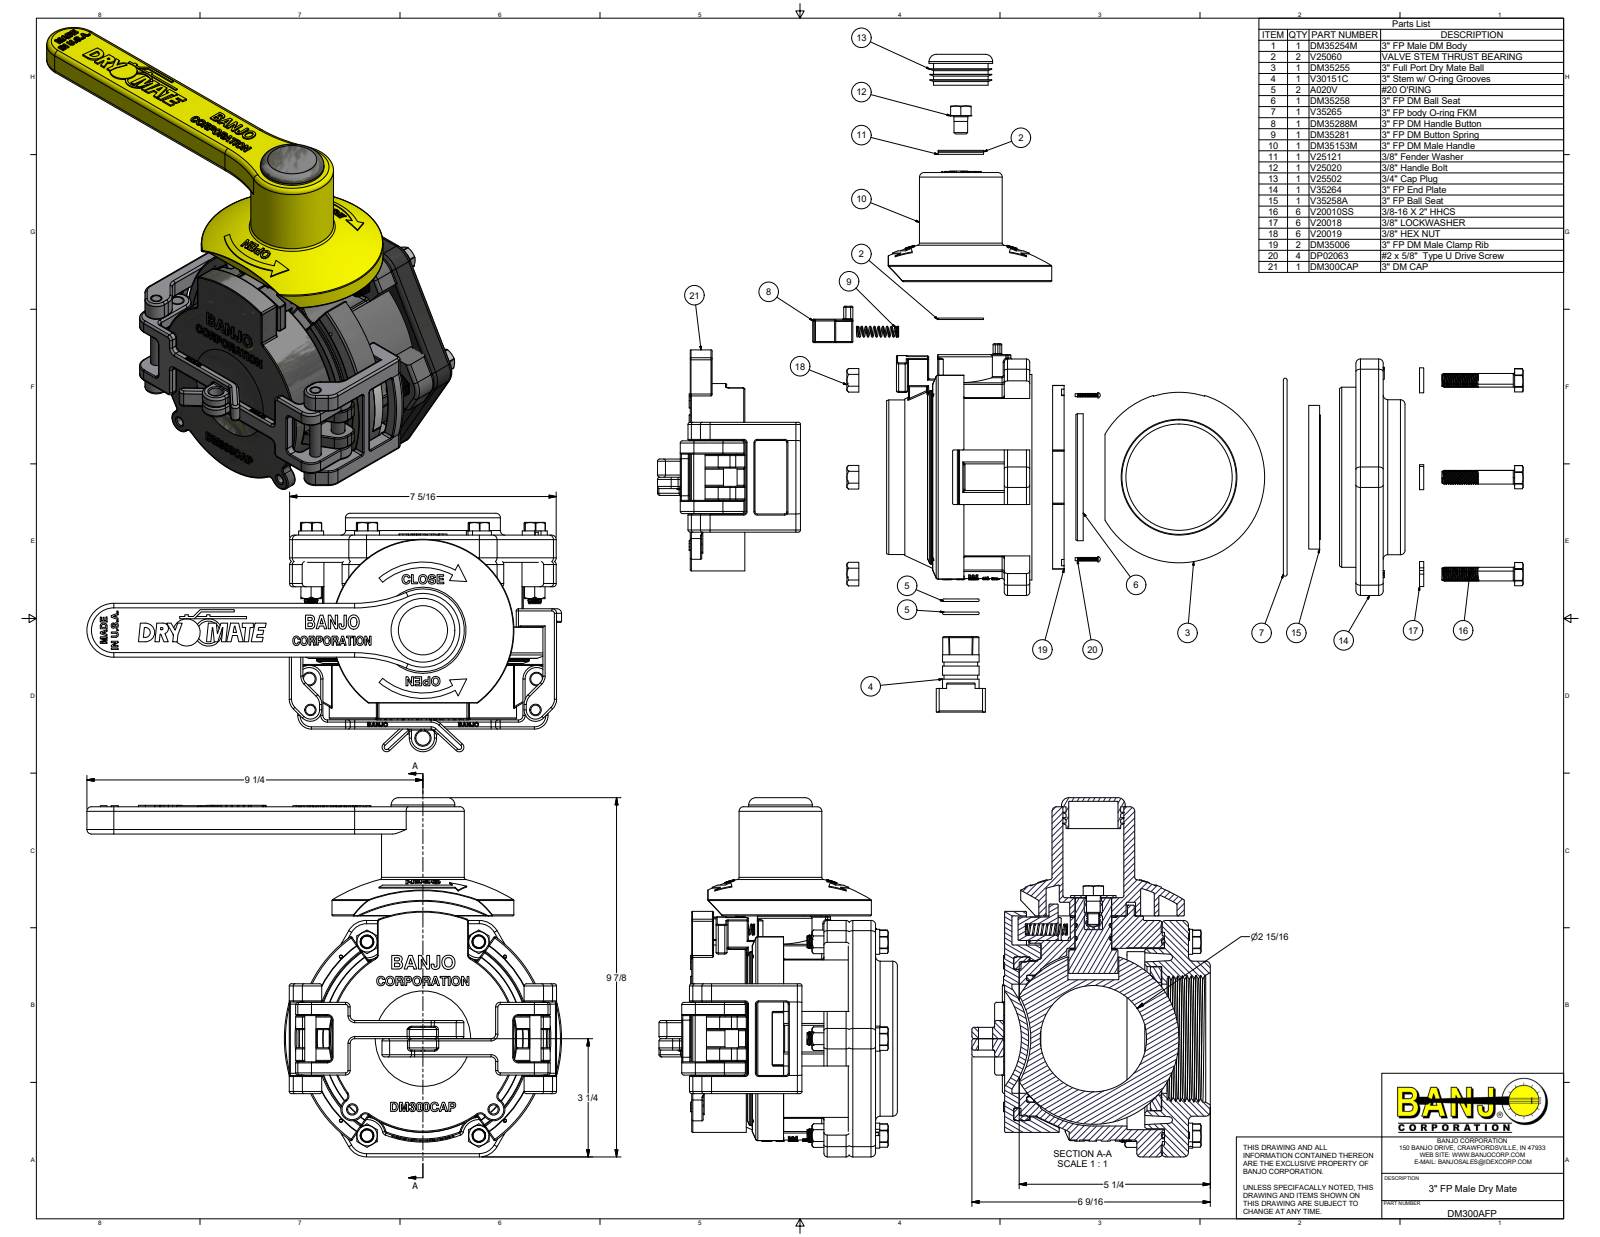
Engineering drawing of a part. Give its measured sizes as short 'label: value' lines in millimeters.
name: DM300AFP; DM35254M; DM35254MY; DM35254MX (+8 more)
written by: Autodesk Inventor 2017 (AUTOMOTIVE_DESIGN)
unit: mm
bodies: 52 solids, 5666 faces (1800 planar, 1481 cylindrical, 2385 other)
size: 331.5 × 250.82 × 166.5
volume: 2 104 000 mm³; area: 590 735 mm²
holes: 7× ⌀7.81, 6× ⌀9.78, 6× ⌀11.18, 4× ⌀2.18, 4× ⌀3.17, 3× ⌀9.52, 2× ⌀6.35, 2× ⌀8, 2× ⌀8.13, 1× ⌀7.8, 1× ⌀7.95, 1× ⌀9.91
bosses: 90× ⌀8.24, 6× ⌀17.46, 6× ⌀9.52, 4× ⌀2.08, 2× ⌀9.78, 2× ⌀8.25, 2× ⌀7.9, 1× ⌀143.51
rounds: 271× R0.76, 118× R1.52, 40× R3.17, 14× R2.29, 14× R9.53, 12× R4.12, 10× R0.25, 8× R0.51
face distances: 128.4, 36.07, 101.47, 0.38, 118.24, 10.16, 6.35, 16.77, 111.63, 17.02
hole spacings: 78.1, 78.11, 135.28, 20.96, 60.93, 80.96, 96.86, 106.93
